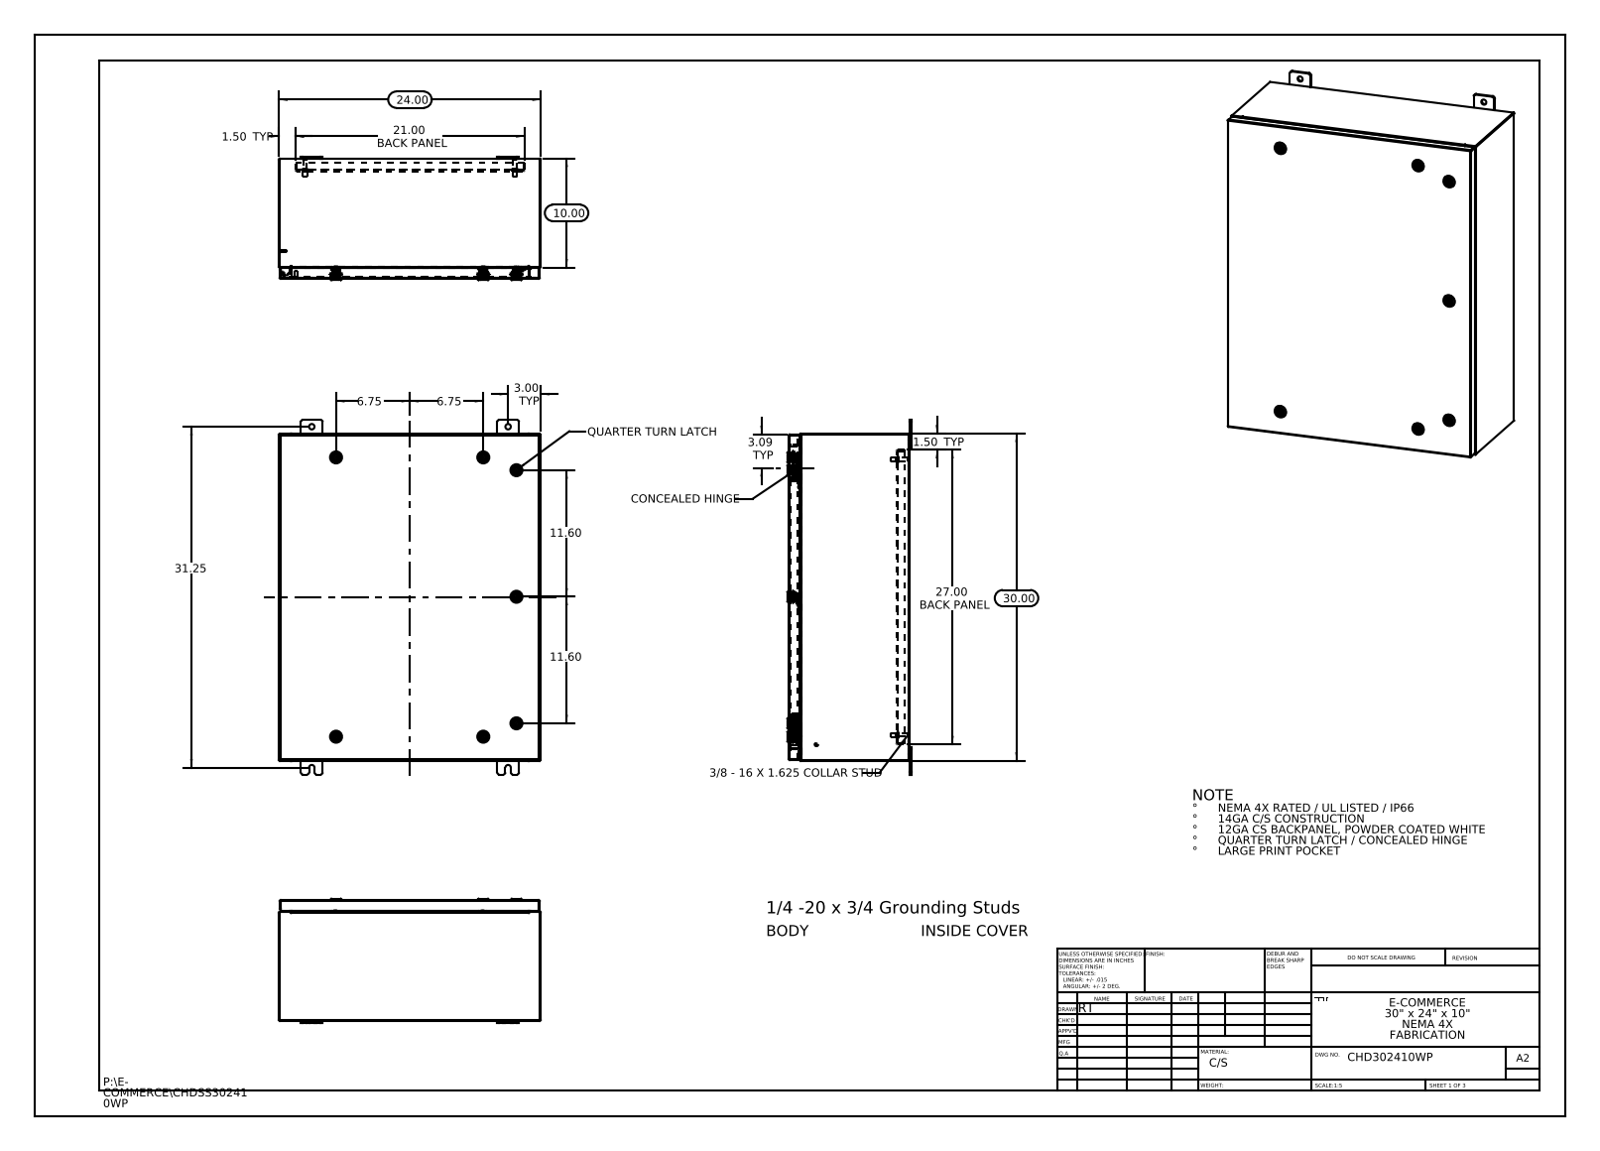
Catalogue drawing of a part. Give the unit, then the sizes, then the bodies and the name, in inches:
Units: inches
Overall size (bounding box): 32.5 × 24 × 11.356
Round holes (diameter × count): ⌀0.5 ×8, ⌀0.197 ×7, ⌀0.394 ×7, ⌀0.4 ×7, ⌀0.63 ×7, ⌀0.787 ×7, ⌀0.136 ×4, ⌀0.211 ×1
Round bosses / shafts (diameter × count): ⌀0.236 ×9, ⌀1.102 ×7, ⌀0.78 ×7, ⌀0.626 ×7, ⌀0.61 ×7, ⌀0.531 ×7, ⌀0.392 ×7, ⌀0.114 ×7
Partial cylindrical surfaces — rounded edges, fillets, slot ends (radius × count): R0.006 ×231, R0.118 ×231, R0.028 ×84, R0.02 ×28, R0.197 ×28, R0.19 ×24, R0.013 ×22, R0.088 ×18
Main face-to-face distances: 0.075, 0.074, 11.01, 10.935, 10.936, 10.861, 0.104, 23.925, 1, 1.075
Hole centre spacings: 0.688, 1.858, 11.6, 13.5, 18, 19.25, 23.687, 25.25
Volume: 283 in³ · Surface area: 7 054 in²
Bodies: 61 solids, 6252 faces (1822 planar, 1948 cylindrical, 2482 other)
Part name (STEP PRODUCT): CHDSS302410WP Backpanel; CHDSS302410WP Cover; CHDSS302410WP Mounting Studs; Concealed Hinge enclosure side (+8 more)
STEP written by: SolidWorks 2013 (CONFIG_CONTROL_DESIGN)
